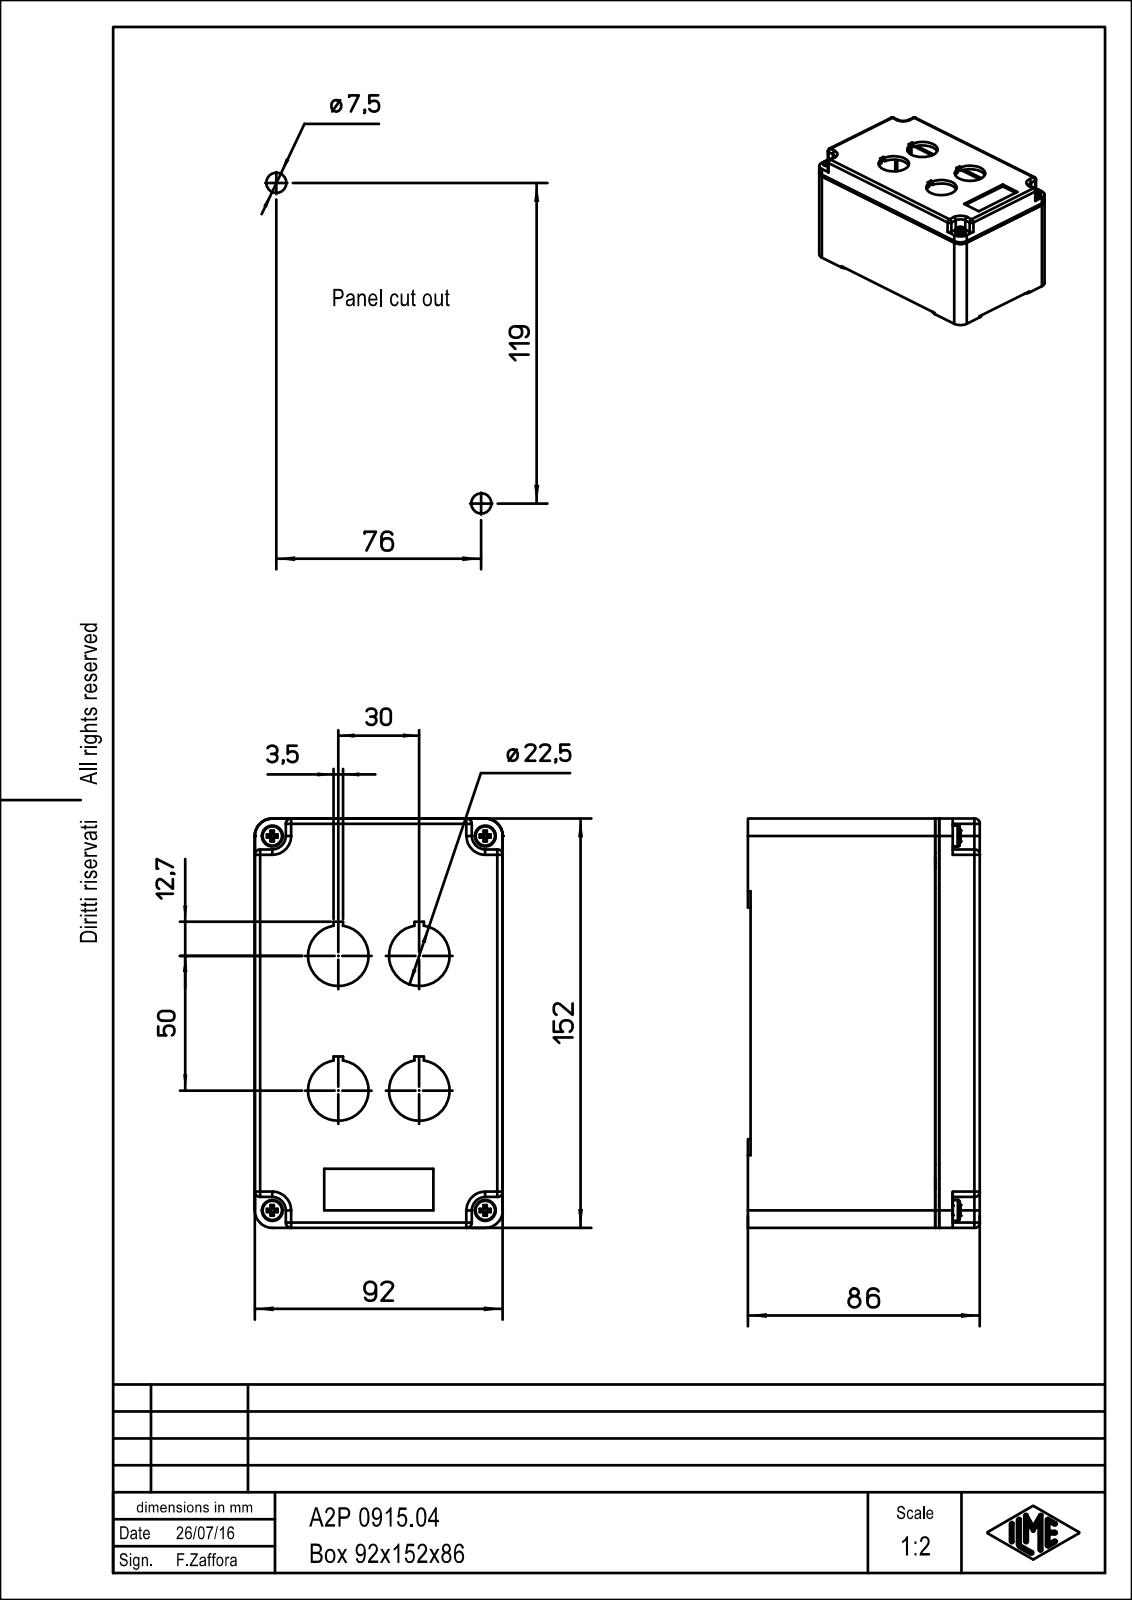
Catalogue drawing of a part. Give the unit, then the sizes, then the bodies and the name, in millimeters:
Units: millimetres
Overall size (bounding box): 152 × 92.02 × 86
Round holes (diameter × count): ⌀3.3 ×6, ⌀4.5 ×4, ⌀22.5 ×4, ⌀5.8 ×2, ⌀7.5 ×2, ⌀10.6 ×1, ⌀10.61 ×1
Round bosses / shafts (diameter × count): ⌀7.8 ×4, ⌀4 ×4, ⌀6.2 ×2, ⌀6 ×2, ⌀7 ×1
Partial cylindrical surfaces — rounded edges, fillets, slot ends (radius × count): R0.33 ×22, R2 ×17, R6 ×12, R6.5 ×12, R5 ×6, R8 ×6, R0.27 ×4, R0.27 ×4
Main face-to-face distances: 3, 82, 4.38, 92, 4.37, 85, 79, 13.5, 65.5, 68.5
Hole centre spacings: 79, 50.8, 70.36, 78.14, 97.62, 109.09, 139, 159.88
Volume: 291 506 mm³ · Surface area: 145 081 mm²
Bodies: 2 solids, 1012 faces (799 planar, 173 cylindrical, 40 other)
Part name (STEP PRODUCT): COVER; BOX; A2P_0915.04
STEP written by: PTC Creo Elements/Direct Modeling 19.0B 21-Mar-2015 (C) Parametric Technology GmbH (AUTOMOTIVE_DESIGN)
